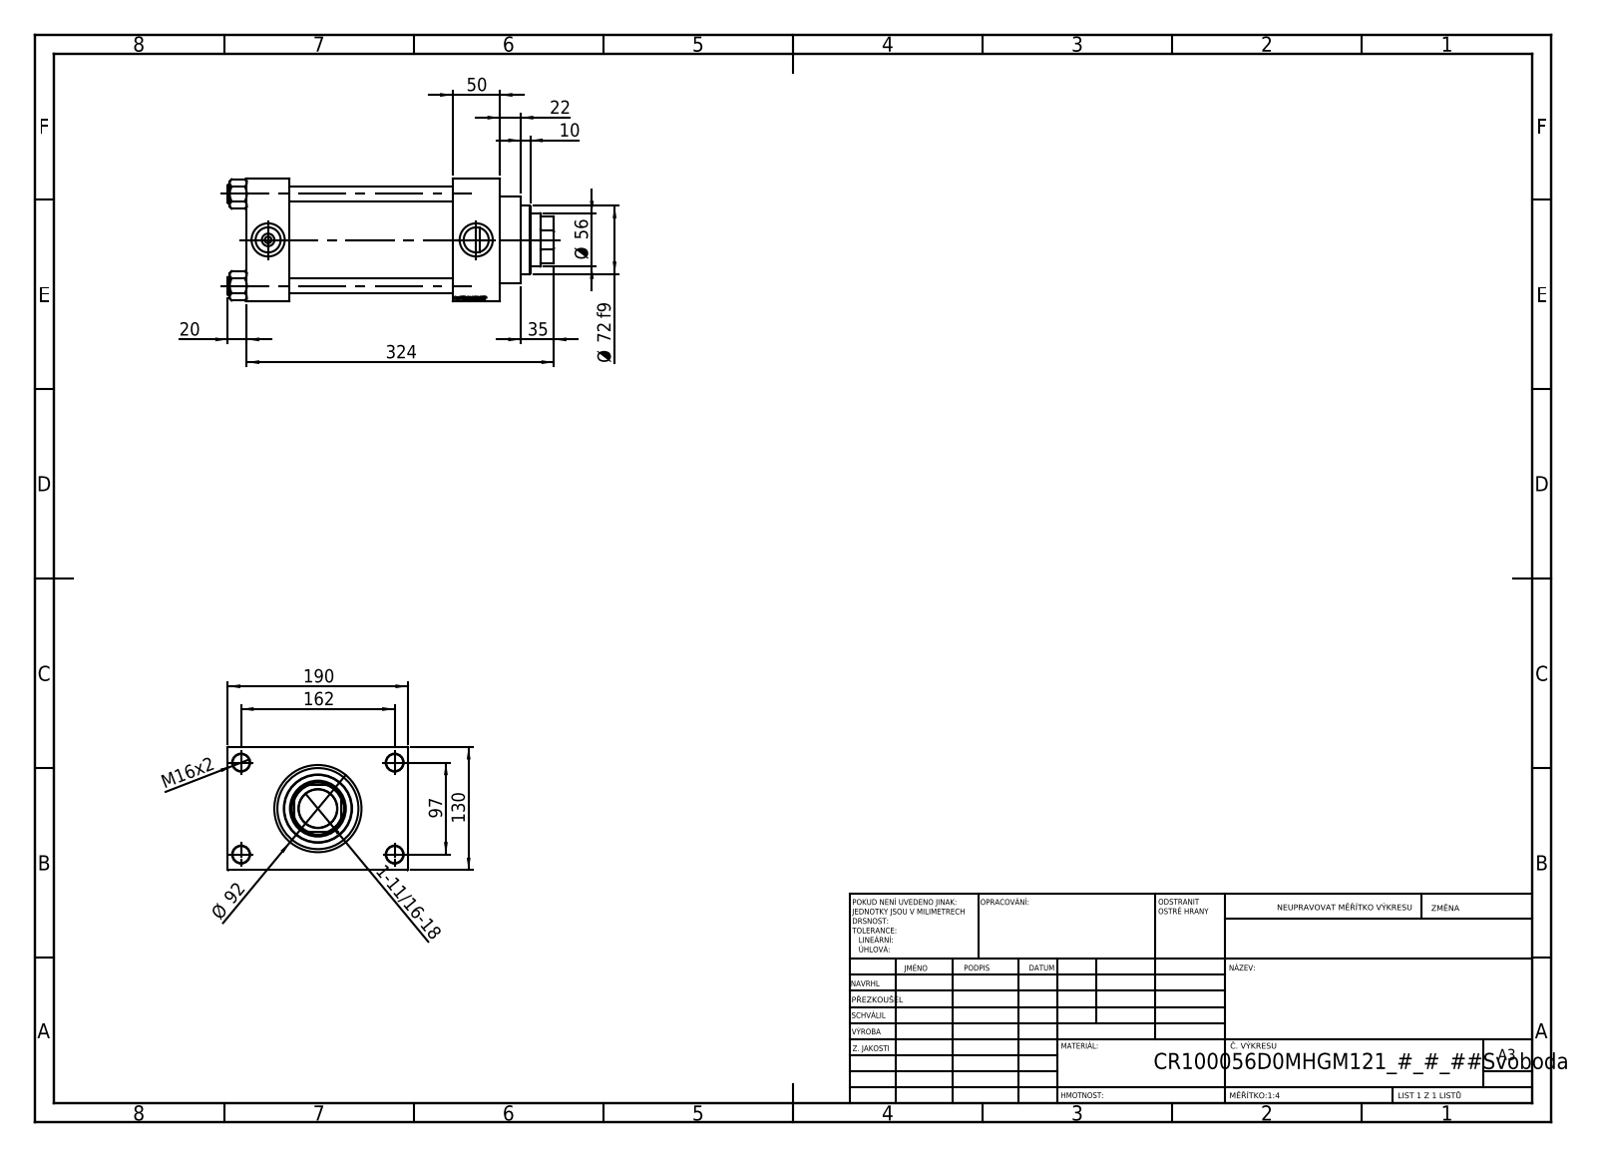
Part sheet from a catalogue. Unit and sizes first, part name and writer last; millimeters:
Units: millimetres
Overall size (bounding box): 344 × 190 × 130
Round holes (diameter × count): ⌀16 ×4, ⌀18 ×4, ⌀7 ×2, ⌀26.44 ×2, ⌀35 ×2, ⌀40.5 ×1, ⌀56 ×1, ⌀59 ×1, ⌀76 ×1, ⌀85.5 ×1, ⌀100 ×1
Round bosses / shafts (diameter × count): ⌀19 ×4, ⌀106 ×1, ⌀92 ×1, ⌀72 ×1
Partial cylindrical surfaces — rounded edges, fillets, slot ends (radius × count): R27 ×1
Main face-to-face distances: 130, 50, 45, 217, 172, 267, 222, 30, 160, 190
Hole centre spacings: 32.55, 68.52, 94.41, 96.9, 102.27, 129.45, 161.73, 97
Volume: 3 056 000 mm³ · Surface area: 465 803 mm²
Bodies: 11 solids, 1151 faces (545 planar, 88 cylindrical, 518 other)
Part name (STEP PRODUCT): V215_VC_A; NUT_M5_D; V215CR_D_TYCINKA; V215CR_D_Body (+1 more)
STEP written by: SolidWorks 2019 (CONFIG_CONTROL_DESIGN)
